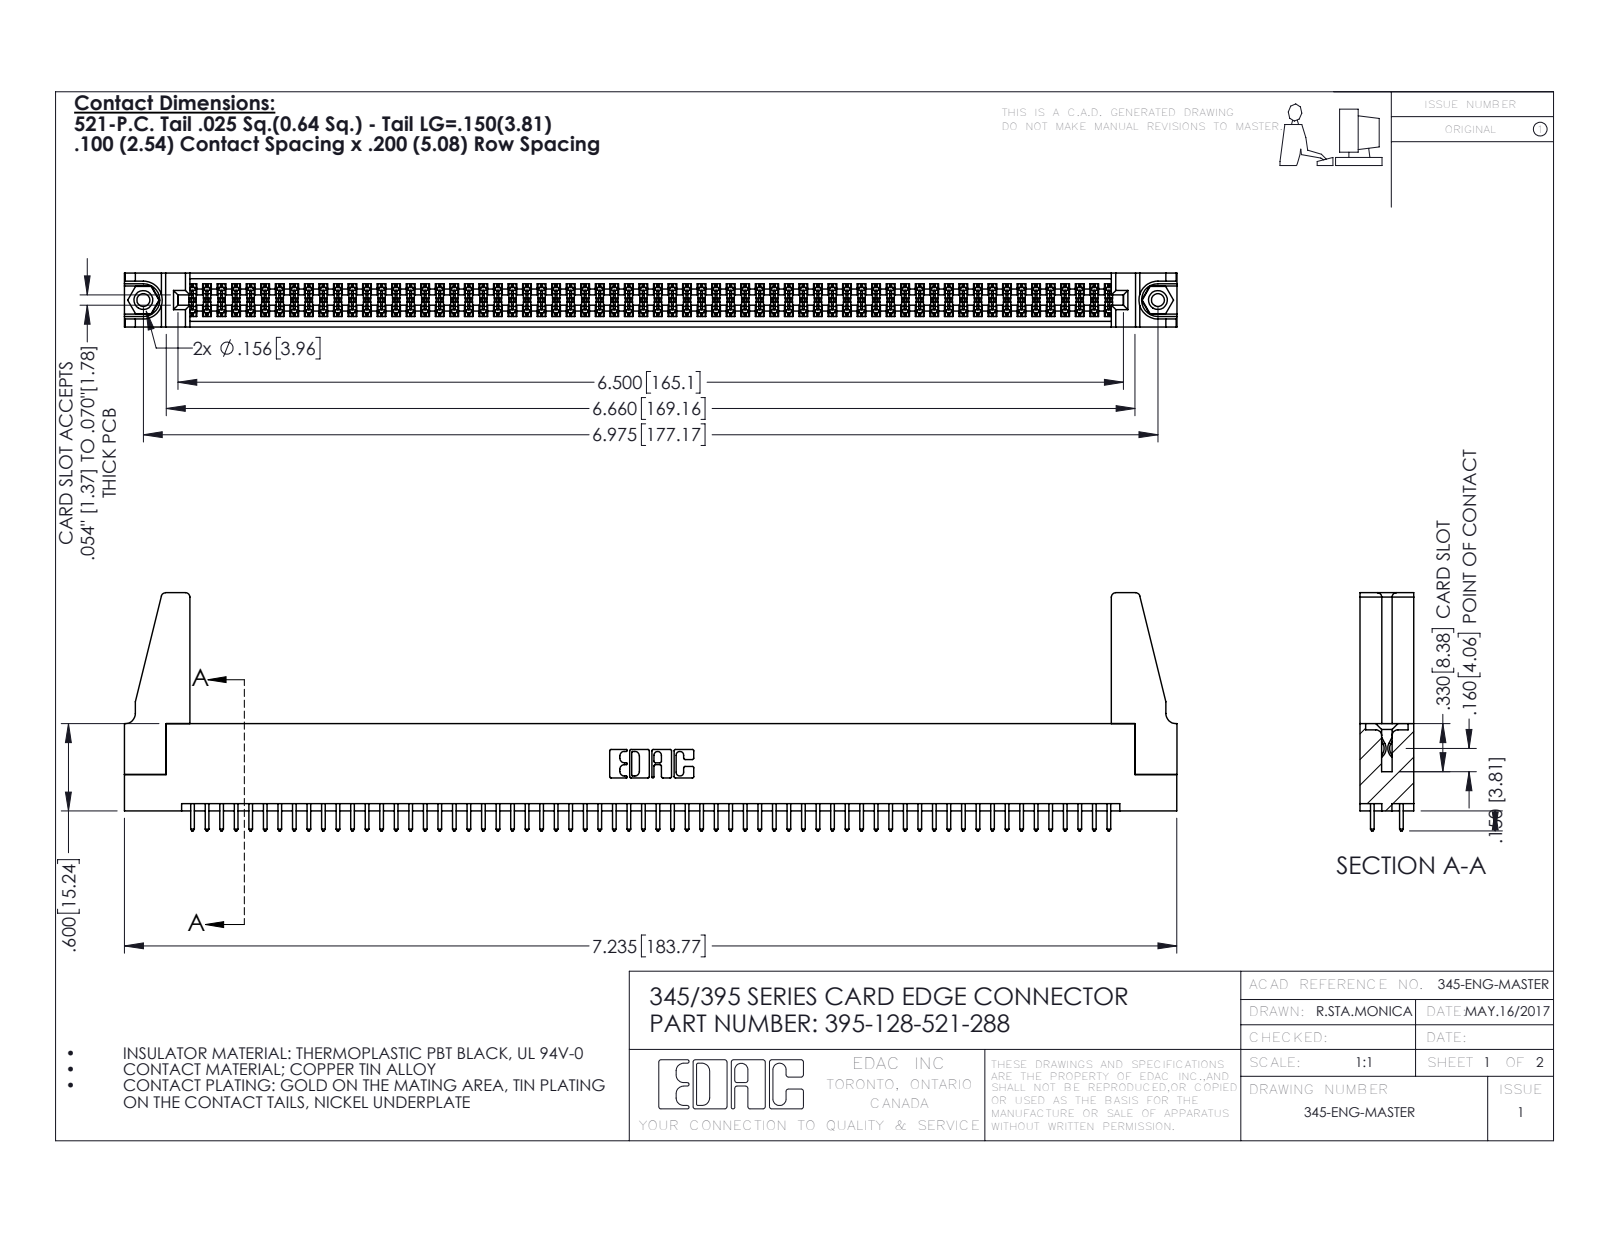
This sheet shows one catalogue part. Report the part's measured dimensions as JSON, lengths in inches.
{"part_name": "395-128-521-288; 345-292-001_345-293-121; 345-220-078_345-220-088; 345-250-001_345-250-001-102 (+1 more)", "step_written_by": "SolidWorks 2016 (CONFIG_CONTROL_DESIGN)", "units": "inches", "bodies": {"solids": 133, "faces": 6650, "planar": 4376, "cylindrical": 2258, "other": 16}, "overall_size": [7.236, 1.637, 0.37], "volume_in3": 1.297, "surface_area_in2": 46.23, "round_holes": [[0.089, 2], [0.125, 2], [0.156, 2], [0.064, 1]], "round_bosses_or_shafts": [[0.155, 2]], "partial_cylinders_radius": [[0.006, 192], [0.01, 128], [0.01, 22], [0.03, 8], [0.007, 6], [0.031, 6], [0.026, 3], [0.014, 2]], "face_to_face_distances": [0.072, 0.298, 0.37, 0.2, 0.098, 0.272, 0.025, 0.225, 0.175, 0.149], "hole_center_spacings": [0.27, 6.739, 6.975]}
